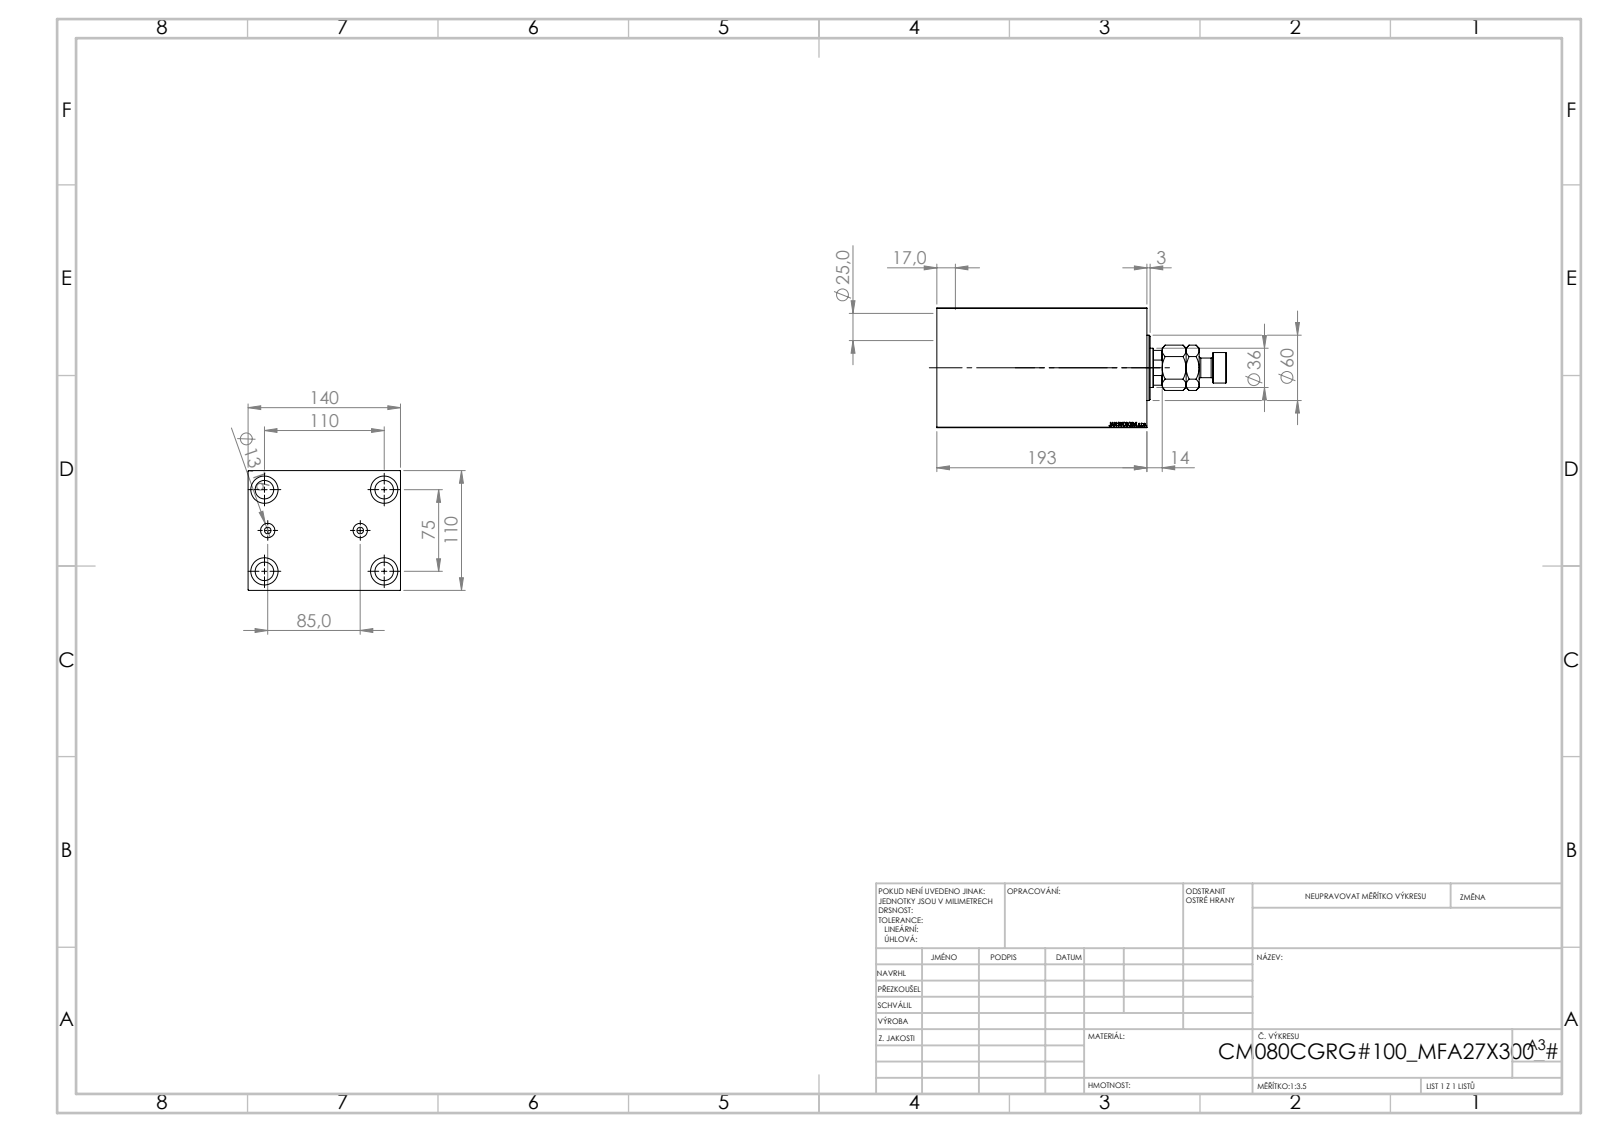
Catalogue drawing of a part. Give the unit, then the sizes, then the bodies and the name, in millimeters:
Units: millimetres
Overall size (bounding box): 266 × 140 × 110
Round holes (diameter × count): ⌀17 ×4, ⌀25 ×4, ⌀6 ×2, ⌀13.16 ×2, ⌀25.5 ×1, ⌀36 ×1, ⌀39.5 ×1, ⌀80 ×1, ⌀82 ×1, ⌀87 ×1
Round bosses / shafts (diameter × count): ⌀60 ×1, ⌀28 ×1, ⌀18 ×1
Partial cylindrical surfaces — rounded edges, fillets, slot ends (radius × count): R17.5 ×1
Main face-to-face distances: 110, 140, 193, 135.75, 57.25, 183, 10, 83, 125.75, 100
Hole centre spacings: 39.53, 66.57, 104.46, 42.5, 75, 110, 133.14, 85
Volume: 2 397 000 mm³ · Surface area: 266 186 mm²
Bodies: 4 solids, 915 faces (427 planar, 62 cylindrical, 426 other)
Part name (STEP PRODUCT): MFA; V450CM_C_Body; V450CM_VC_B; V450CM_C_VCP
STEP written by: SolidWorks 2019 (CONFIG_CONTROL_DESIGN)
